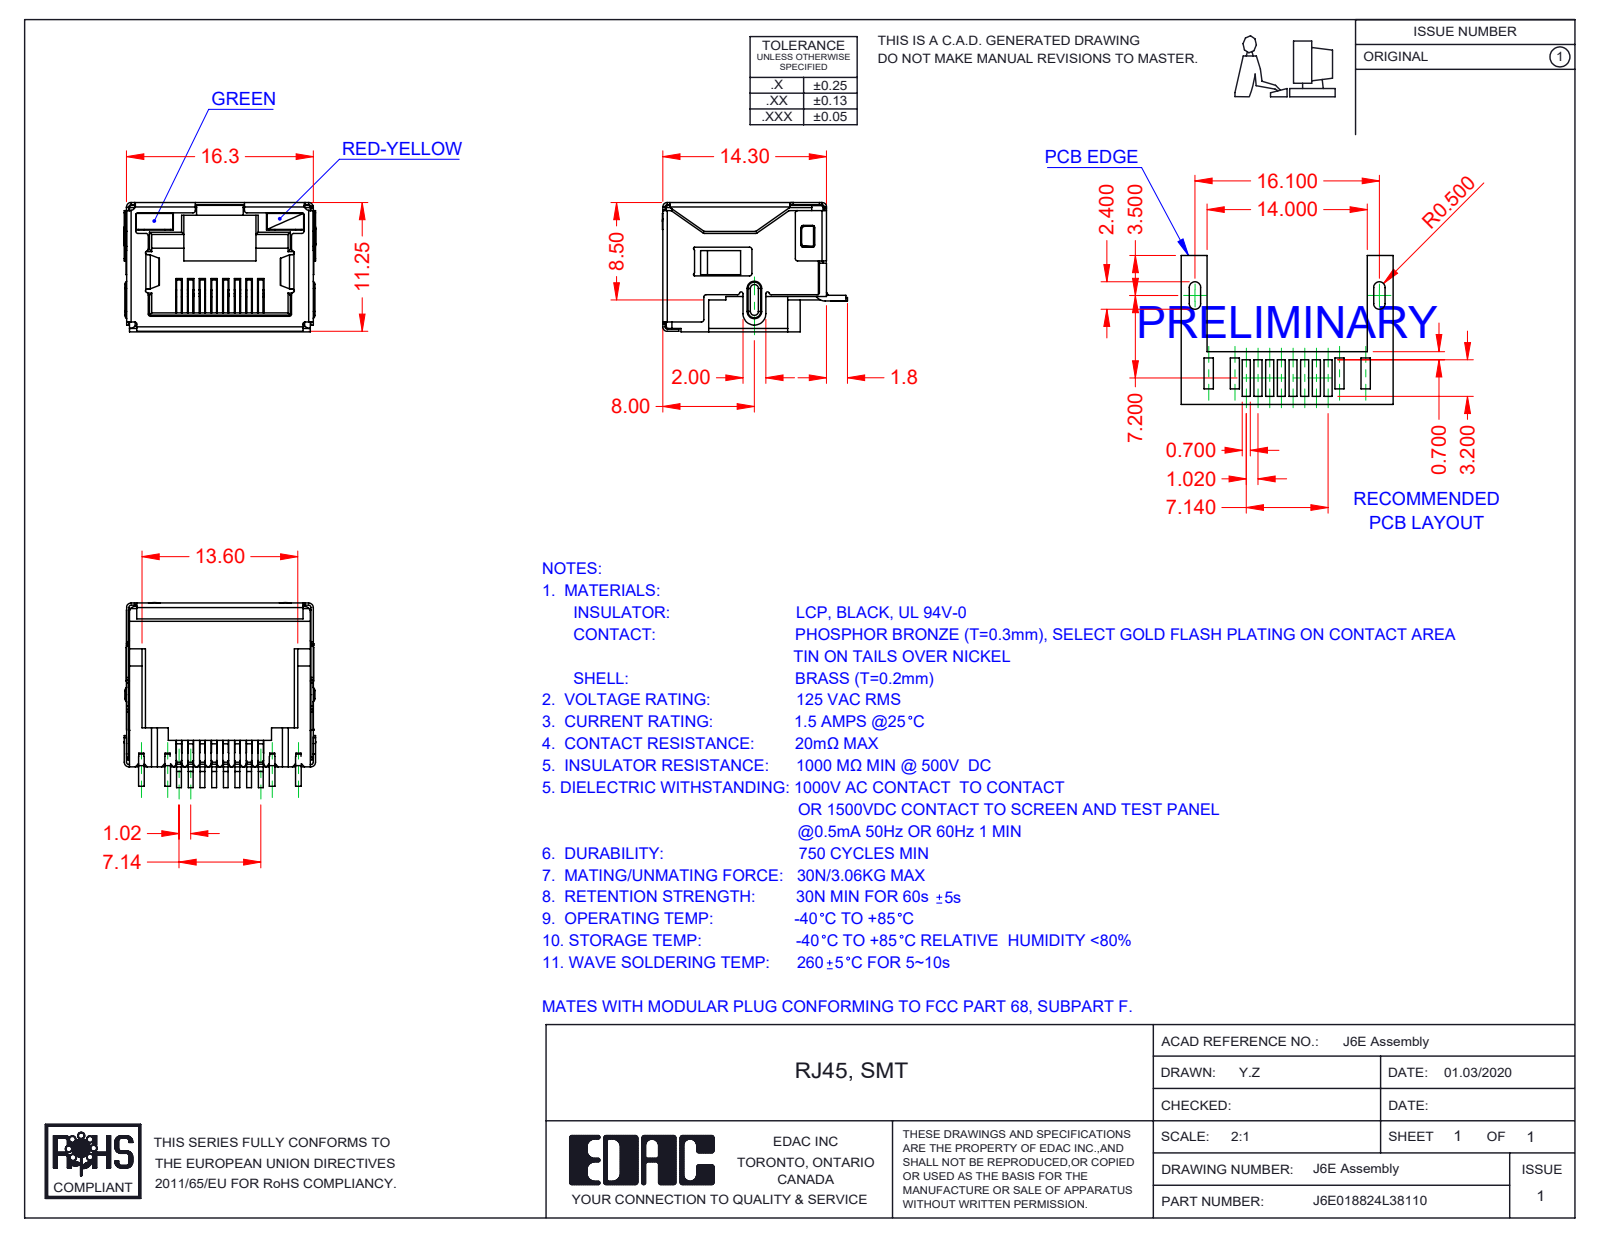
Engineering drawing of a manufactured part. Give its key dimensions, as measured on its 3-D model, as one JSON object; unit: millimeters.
{"part_name": "6E Shield_LED; 6E LED RH_8-Red-Yellow; 6E Contacts; 6E LED LH_3-Green (+2 more)", "step_written_by": "SolidWorks 2016 (CONFIG_CONTROL_DESIGN)", "units": "millimeters", "bodies": {"solids": 12, "faces": 1498, "planar": 1099, "cylindrical": 349, "other": 50}, "overall_size": [16.75, 16.15, 11.3], "volume_mm3": 1109, "surface_area_mm2": 4045, "partial_cylinders_radius": [[0.2, 82], [0.25, 17], [0.4, 13], [0.5, 13], [0.1, 10], [0.15, 7], [0.3, 4], [1, 3]], "face_to_face_distances": [11.05, 16.05, 16.1, 15.85, 11.1, 11.3, 2.4, 0.7, 9.85, 0.49]}
